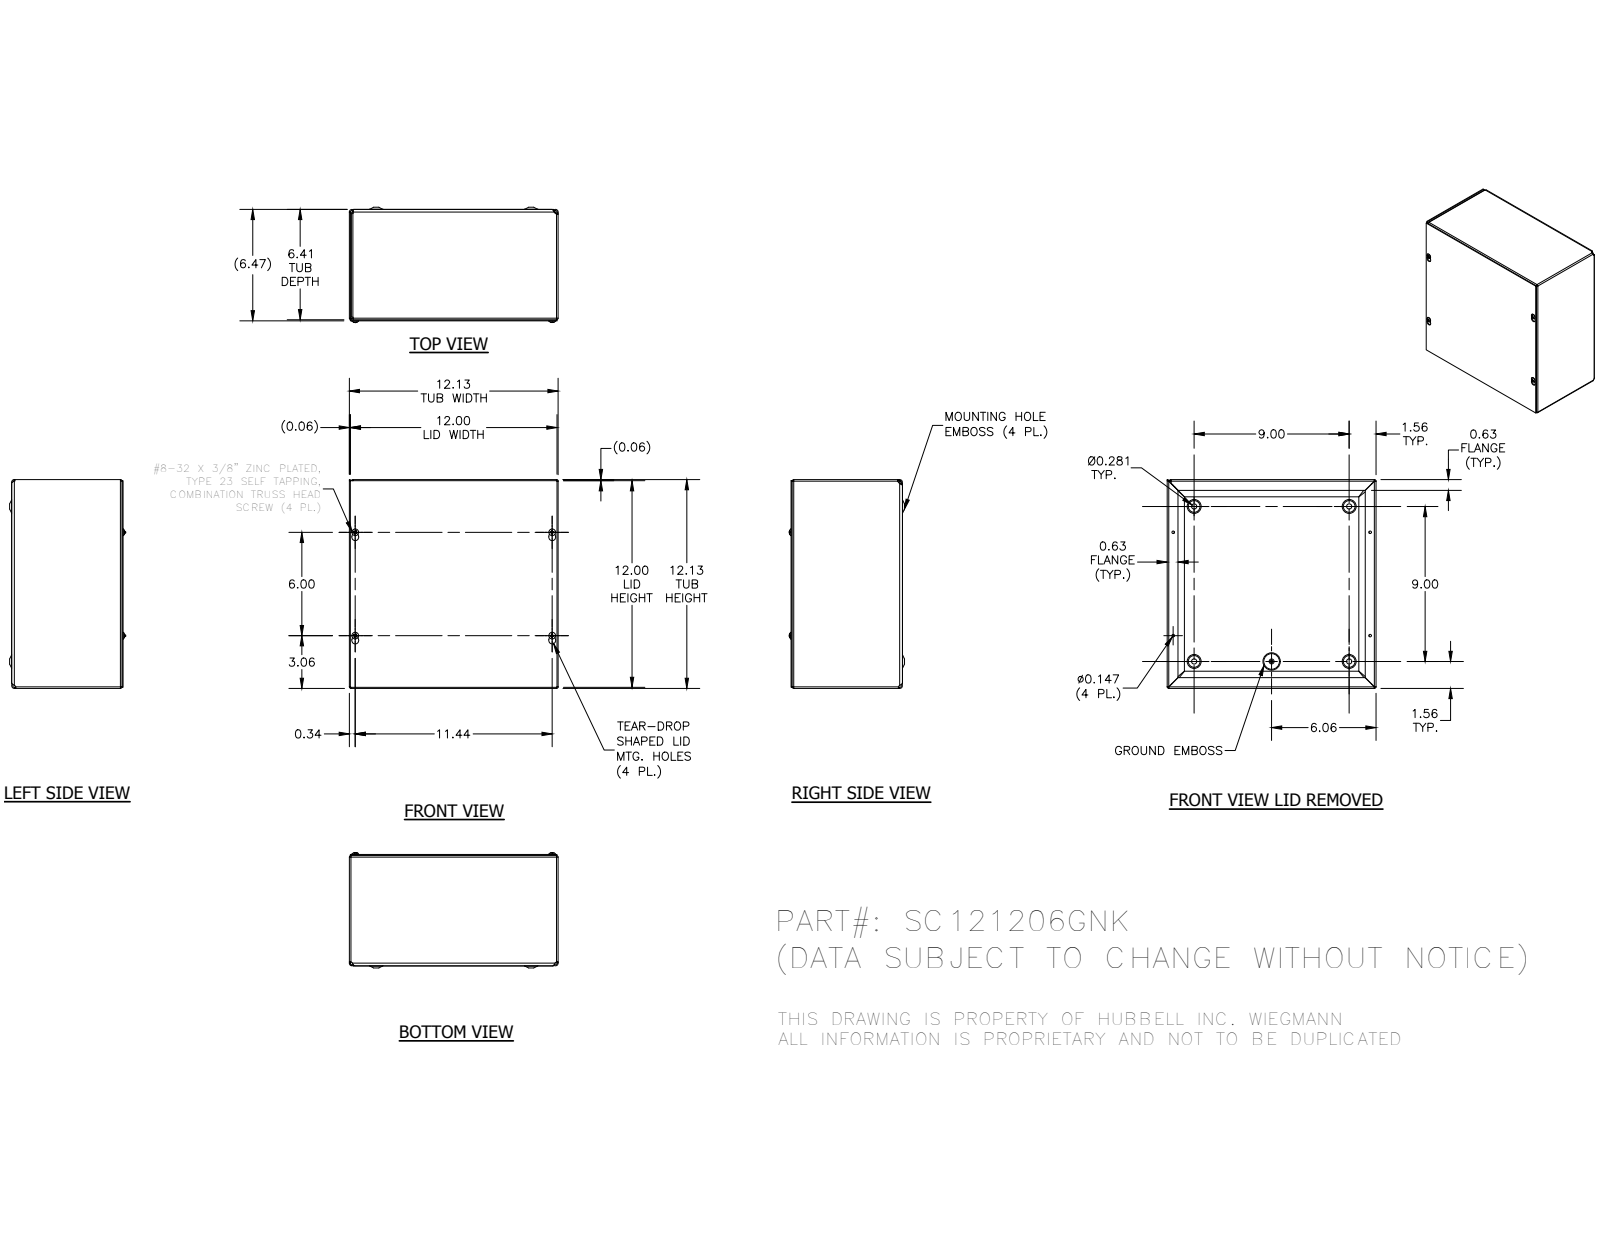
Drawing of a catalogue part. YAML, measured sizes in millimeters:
part_name: "SC1212GNKBKP; SC121206GNKWRA; SC1212GNKLID; 34056 (+1 more)"
step_written_by: "Autodesk Inventor 2014 (AUTOMOTIVE_DESIGN)"
units: millimeters
bodies: {solids: 7, faces: 358, planar: 133, cylindrical: 73, other: 152}
overall_size: [307.98, 307.98, 170]
volume: 666281
surface_area: 854238
round_holes:
  - {diameter: 3.73, count: 4}
  - {diameter: 7.62, count: 4}
  - {diameter: 4.19, count: 1}
round_bosses_or_shafts:
  - {diameter: 9.75, count: 4}
  - {diameter: 4.17, count: 4}
  - {diameter: 5.8, count: 1}
partial_cylinders:
  - {radius: 0.79, count: 8}
  - {radius: 2.37, count: 8}
  - {radius: 1.4, count: 4}
  - {radius: 1.57, count: 4}
  - {radius: 2.38, count: 4}
  - {radius: 2.97, count: 4}
  - {radius: 3.15, count: 4}
  - {radius: 3.17, count: 4}
face_to_face_distances: [1.57, 306.4, 161.12, 304.83, 162.69, 1.59, 162.71, 164.28, 1.58, 307.97]
hole_center_spacings: [228.6, 114.3, 152.4, 192.98, 193.02, 255.58, 262.33, 262.34]
